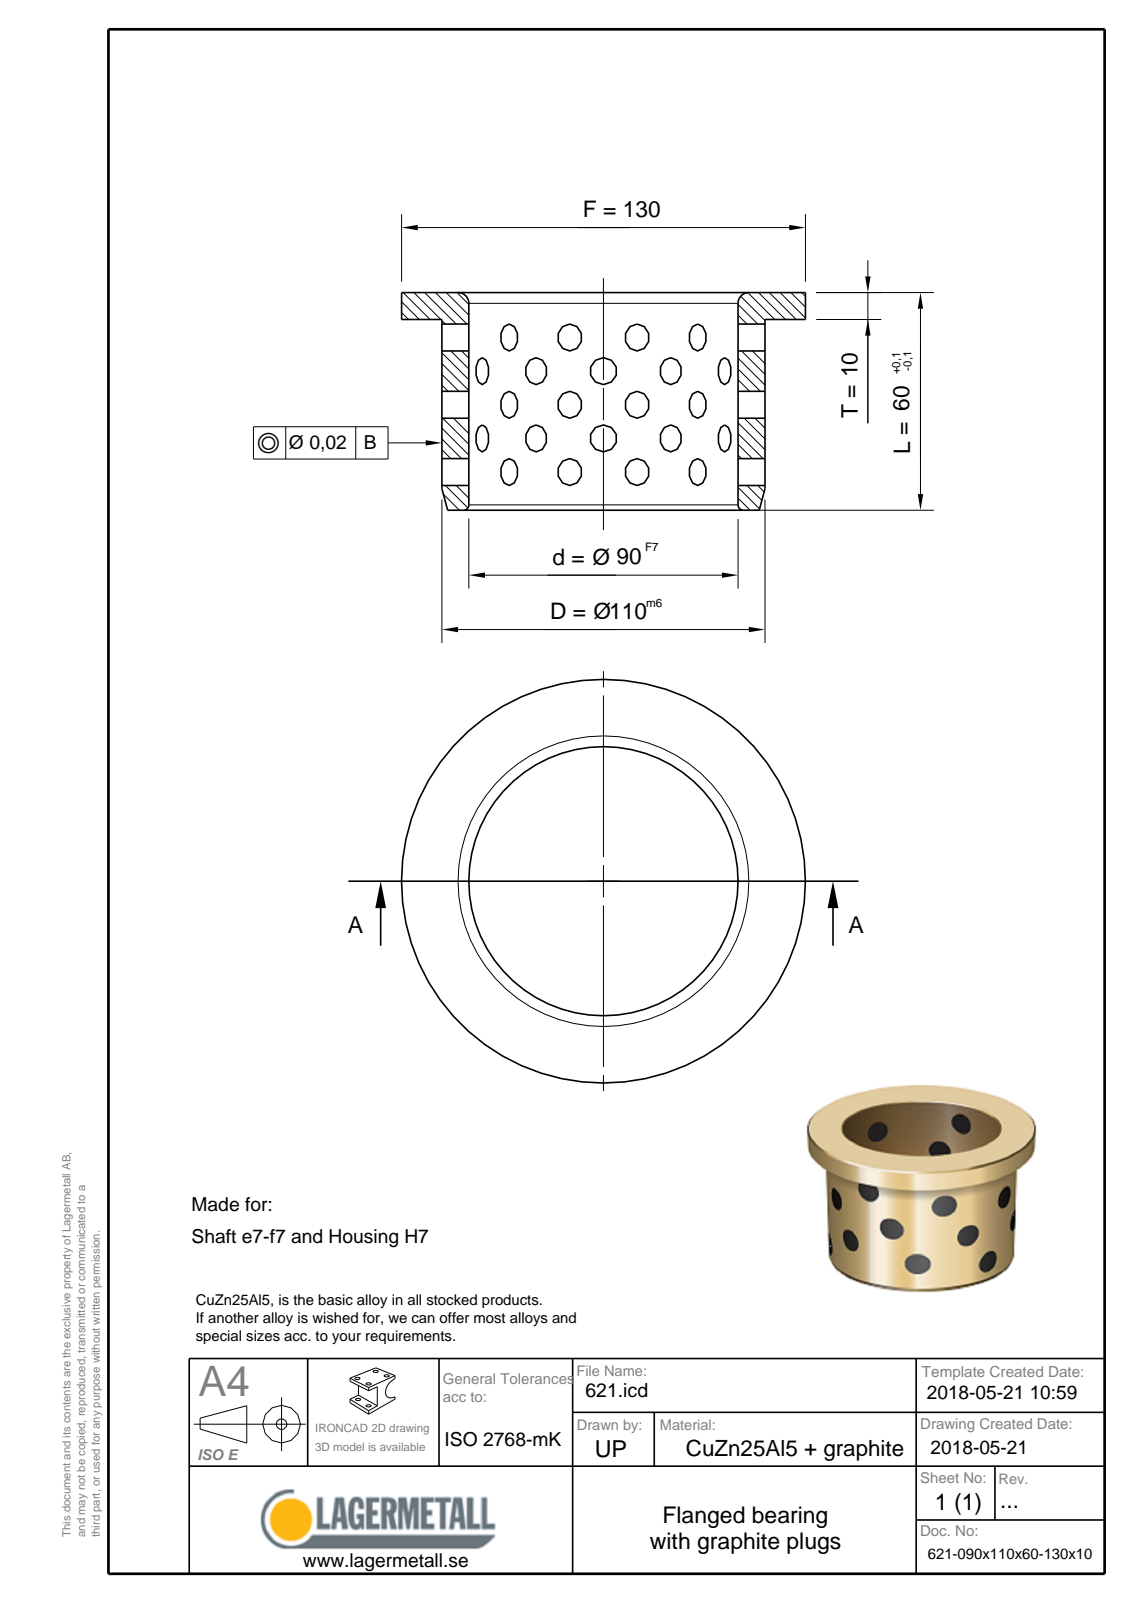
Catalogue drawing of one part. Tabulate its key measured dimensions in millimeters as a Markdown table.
| quantity | value |
| --- | --- |
| part name | 621-090x110x60-130x10 |
| STEP written by | Spatial InterOp 3D (CONFIG_CONTROL_DESIGN) |
| units | millimeters |
| bodies | 1 solid, 9 faces (3 planar, 3 cylindrical, 3 other) |
| overall size | 130 × 130 × 60 |
| volume | 224 660 mm³ |
| surface area | 51 151 mm² |
| round holes (diameter × count) | 90 × 1 |
| round bosses / shafts (diameter × count) | 130 × 1, 110 × 1 |
| main face-to-face distances | 10, 50, 60 |
